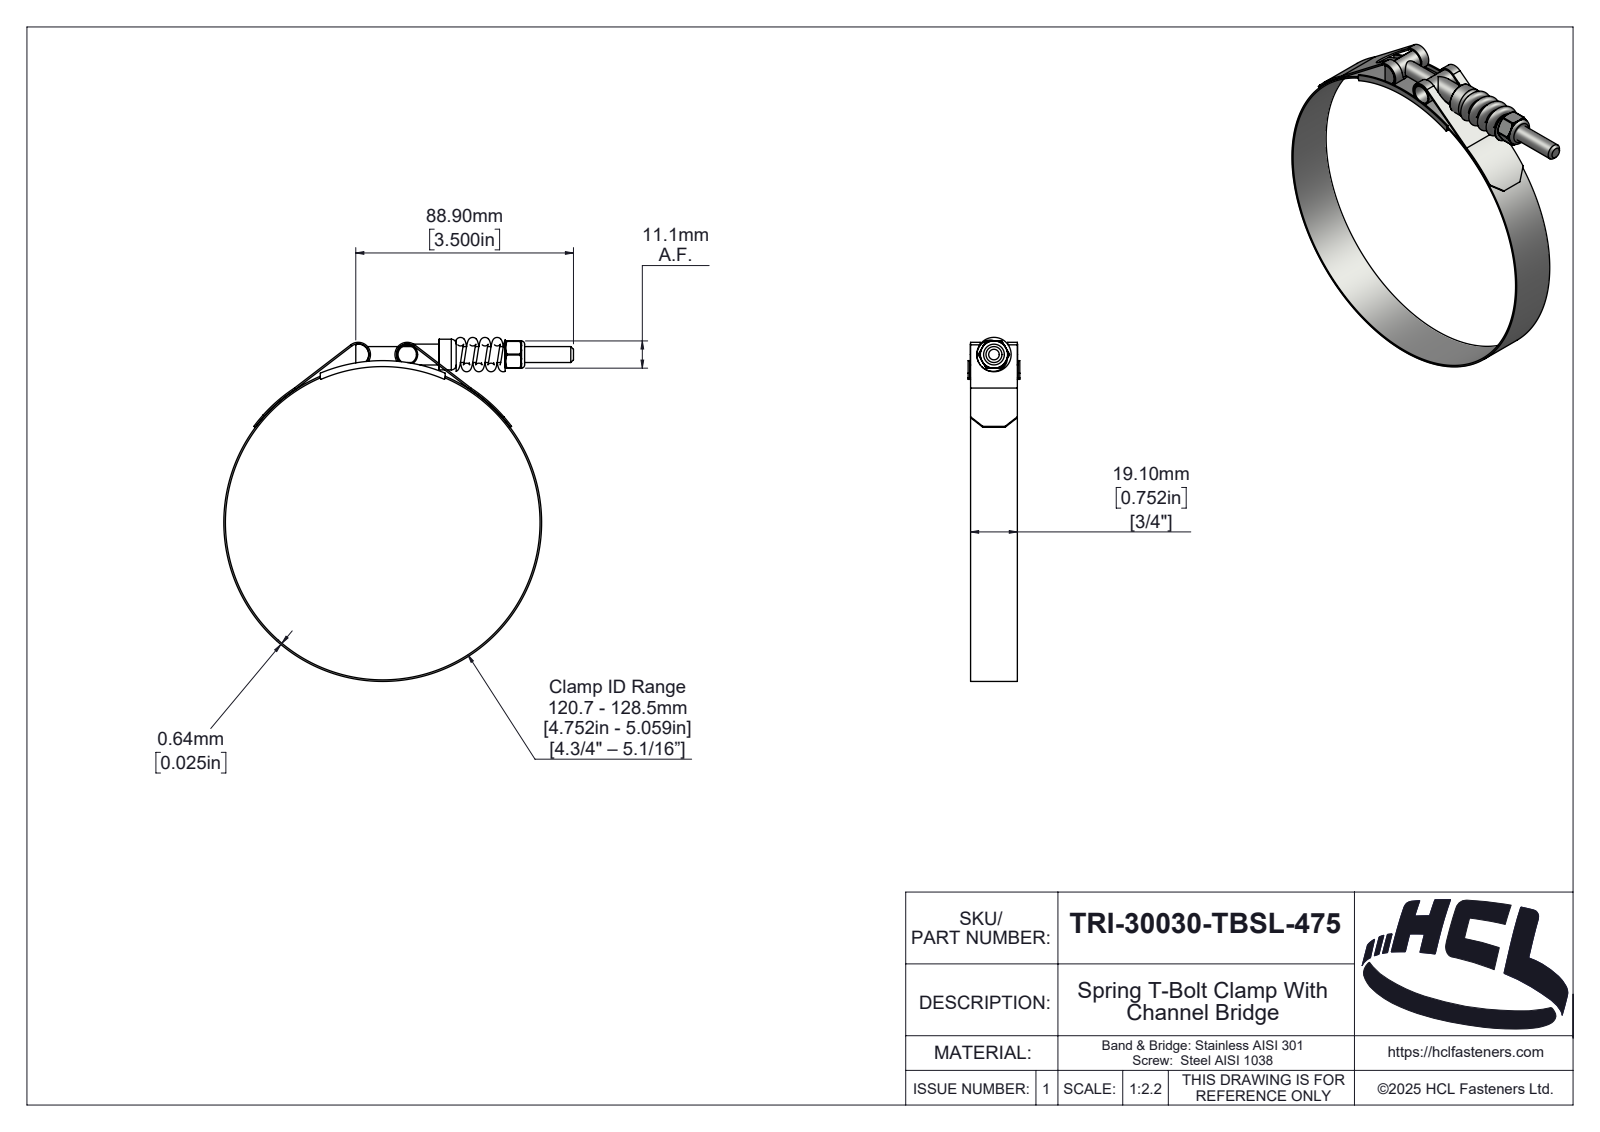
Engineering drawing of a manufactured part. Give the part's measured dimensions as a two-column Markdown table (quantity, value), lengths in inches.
| quantity | value |
| --- | --- |
| part name | TRI-30030-TBSL-475 |
| STEP written by | SolidWorks 2025 (AUTOMOTIVE_DESIGN) |
| units | inches |
| bodies | 7 solids, 332 faces (48 planar, 122 cylindrical, 162 other) |
| overall size | 5.661 × 5.529 × 0.831 |
| volume | 0.811 in³ |
| surface area | 44.74 in² |
| round holes (diameter × count) | 0.213 × 1, 0.25 × 1, 0.256 × 1, 0.296 × 1, 5.059 × 1 |
| round bosses / shafts (diameter × count) | 0.335 × 2, 5.109 × 1, 0.493 × 1 |
| partial cylindrical surfaces (radius × count) | 0.015 × 6, 0.02 × 2, 0.172 × 2, 0.197 × 2, 0.023 × 1, 0.095 × 1, 0.119 × 1, 0.126 × 1 |
| main face-to-face distances | 0.025, 0.752, 0.039, 0.791, 0.806, 0.014, 0.766, 0.831, 2.402, 0.437 |
| hole center spacings | 2.726 |
